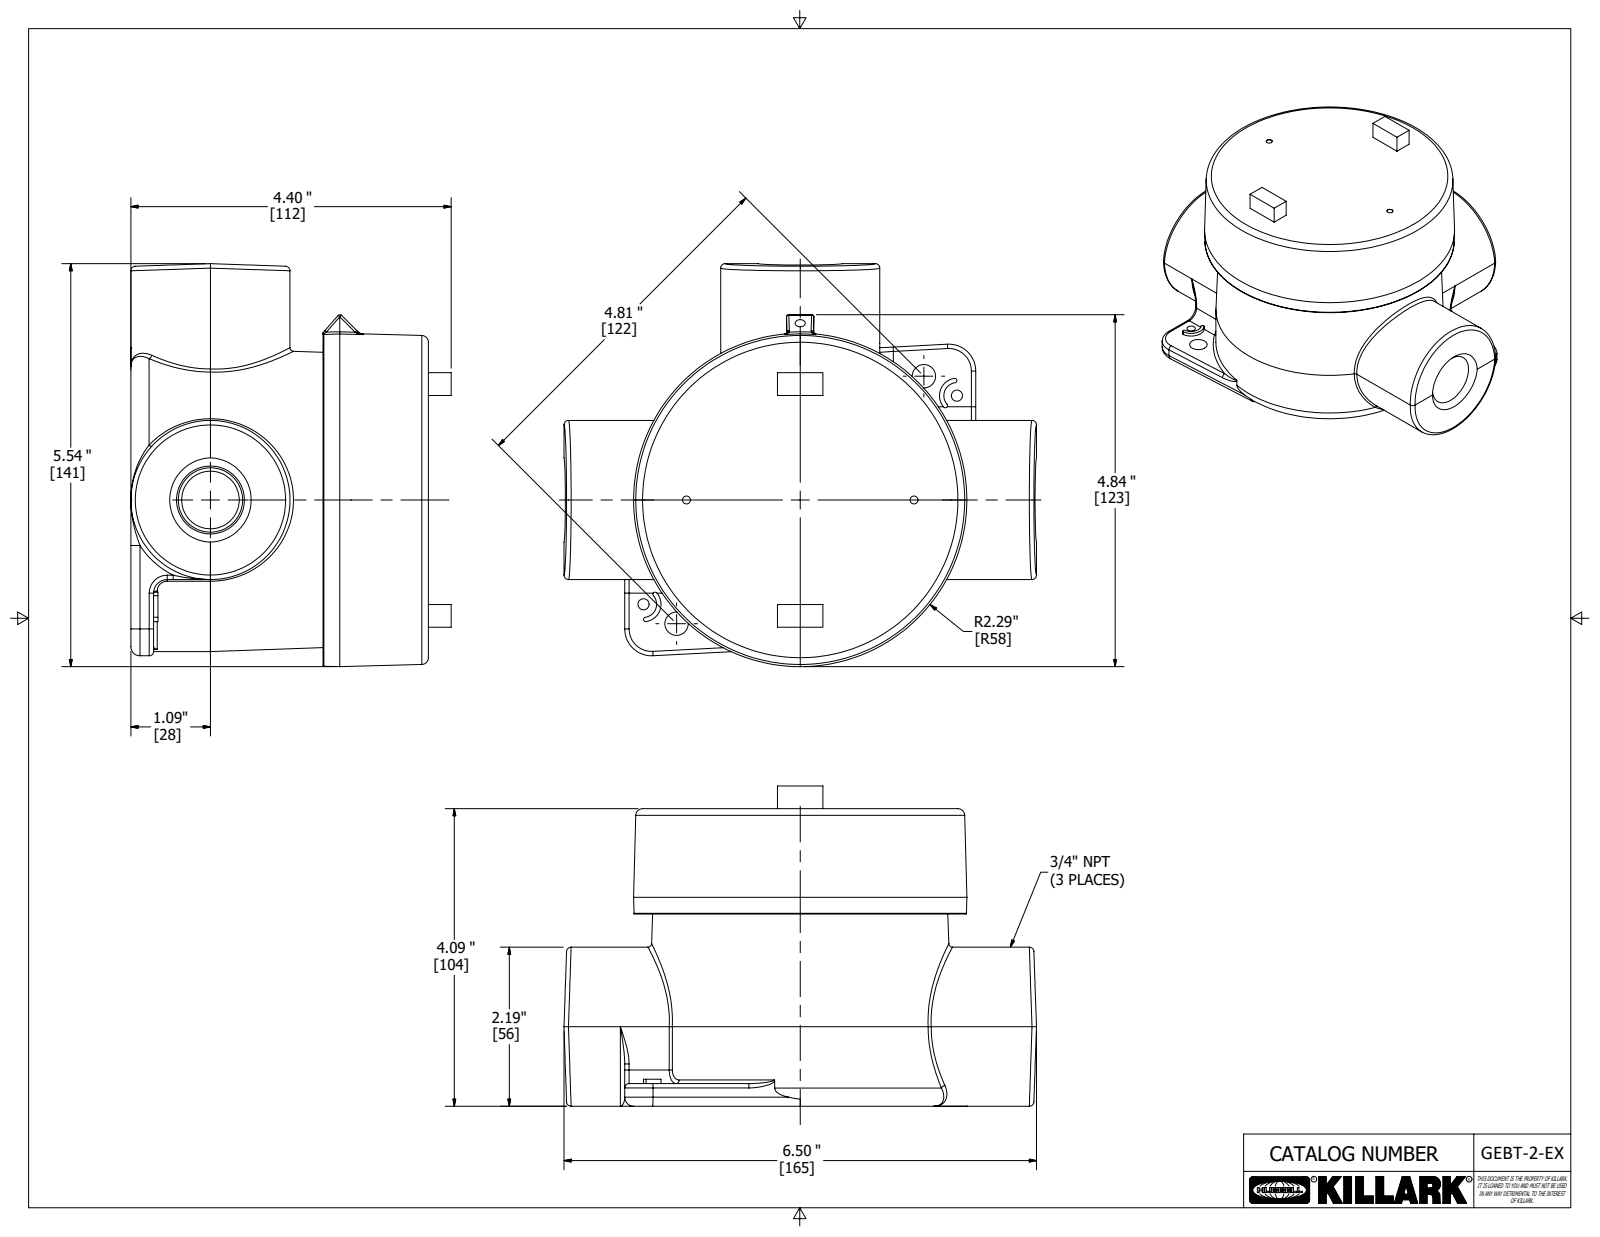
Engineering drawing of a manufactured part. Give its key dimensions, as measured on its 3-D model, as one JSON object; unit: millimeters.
{"part_name": "GEBT-2-EX; 21155; 23649AAAM", "step_written_by": "Autodesk Inventor 2020 (AUTOMOTIVE_DESIGN)", "units": "millimeters", "bodies": {"solids": 2, "faces": 854, "planar": 415, "cylindrical": 98, "other": 341}, "overall_size": [231.1, 140.8, 111.9], "volume_mm3": 669900, "surface_area_mm2": 137900, "round_holes": [[2.8, 2], [3.9, 2], [8.2, 2], [20.1, 2], [39.6, 2], [3.5, 1], [97.1, 1], [102.7, 1]], "round_bosses_or_shafts": [[55.6, 2]], "partial_cylinders_radius": [[1.5, 35], [0.8, 14], [3.2, 4], [0.8, 3], [4.7, 3], [4.6, 2], [6.1, 2], [9.4, 2]], "face_to_face_distances": [104, 92.8, 11.1, 88.9, 3.9, 15.1, 67.2, 21.7, 25.7, 36.8], "hole_center_spacings": [13.4, 39.4, 39.8, 43.4, 61.1, 65.8, 93.5, 101.3]}
